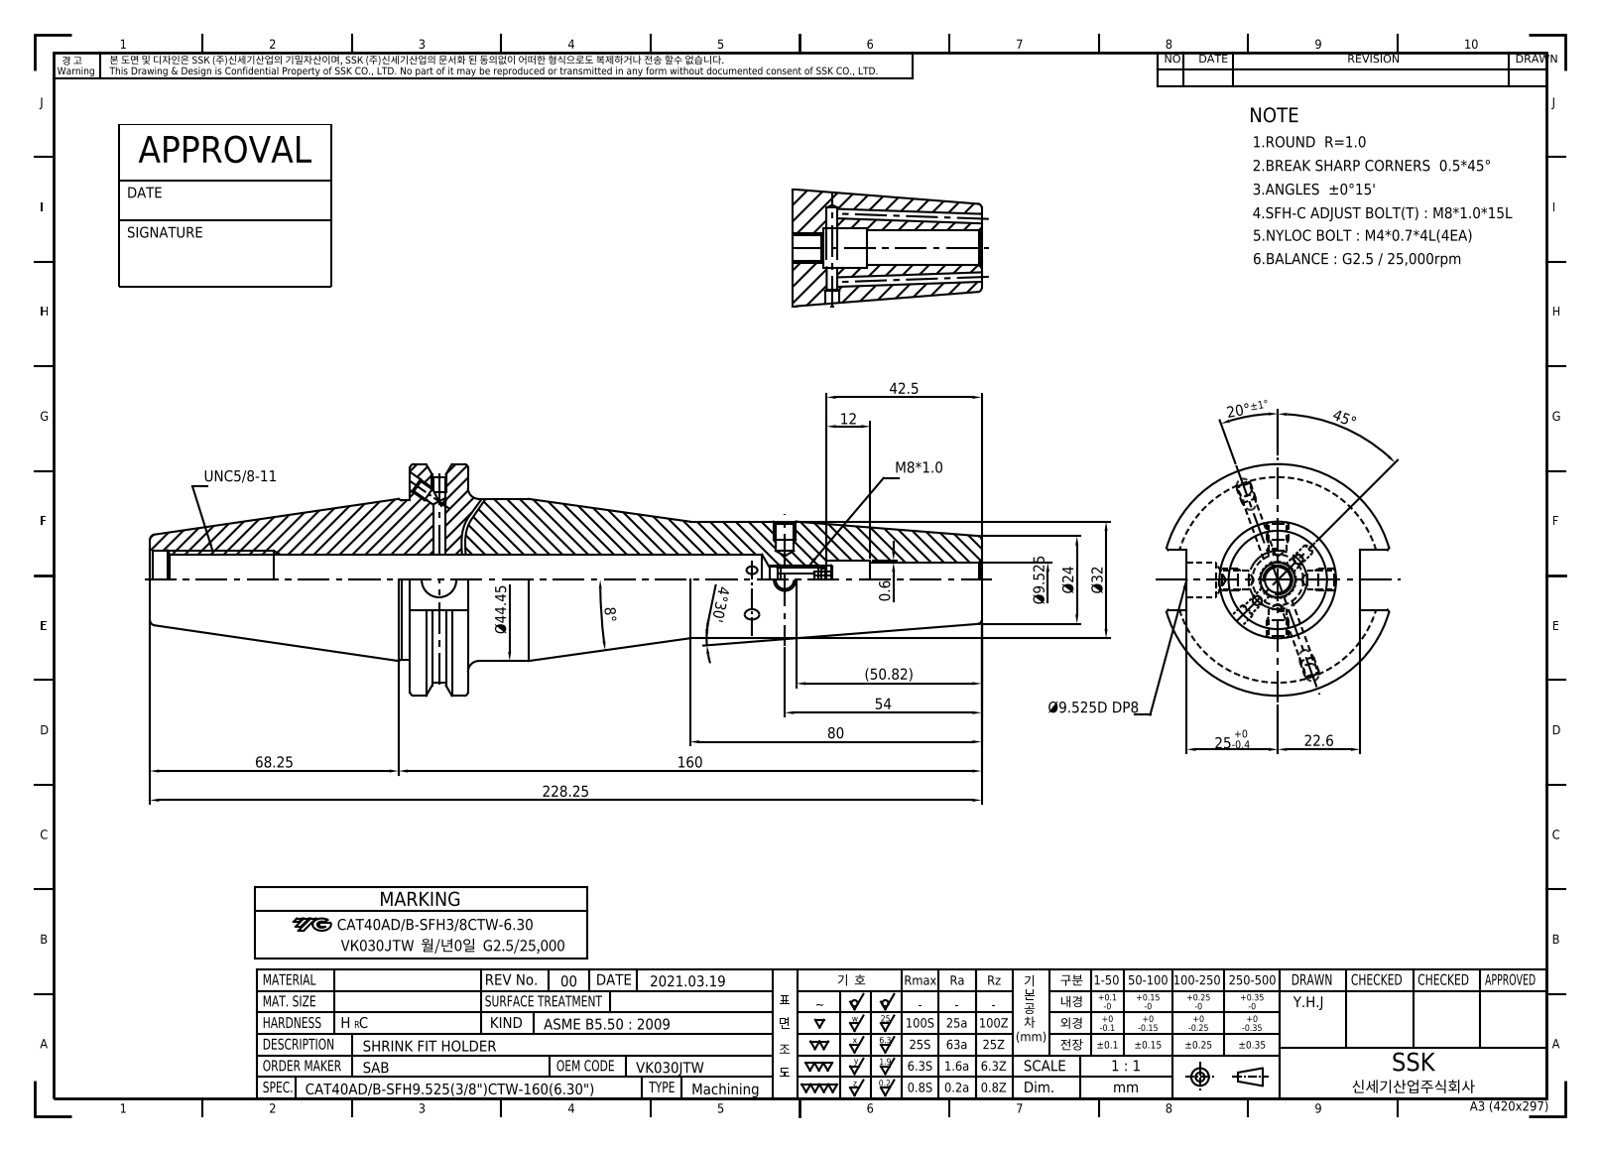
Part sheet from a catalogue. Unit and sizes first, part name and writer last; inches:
Units: inches
Overall size (bounding box): 8.986 × 2.5 × 2.405
Round holes (diameter × count): ⌀0.128 ×4, ⌀0.079 ×2, ⌀0.157 ×2, ⌀0.165 ×2, ⌀0.375 ×2, ⌀0.272 ×1, ⌀0.422 ×1, ⌀0.512 ×1, ⌀0.527 ×1, ⌀0.642 ×1
Round bosses / shafts (diameter × count): ⌀2.5 ×1, ⌀1.75 ×1, ⌀1.717 ×1, ⌀1.26 ×1
Partial cylindrical surfaces — rounded edges, fillets, slot ends (radius × count): R1.108 ×1
Main face-to-face distances: 0.625, 6.174, 5.549, 1.874, 0.645, 2.812, 3.437, 8.986, 3.05, 0.238
Volume: 13.3 in³ · Surface area: 62.54 in²
Bodies: 1 solid, 91 faces (37 planar, 32 cylindrical, 22 other)
Part name (STEP PRODUCT): LO-CAT40ADB-SFH9.525CTW-160
STEP written by: Autodesk Inventor 2024 (AUTOMOTIVE_DESIGN)
